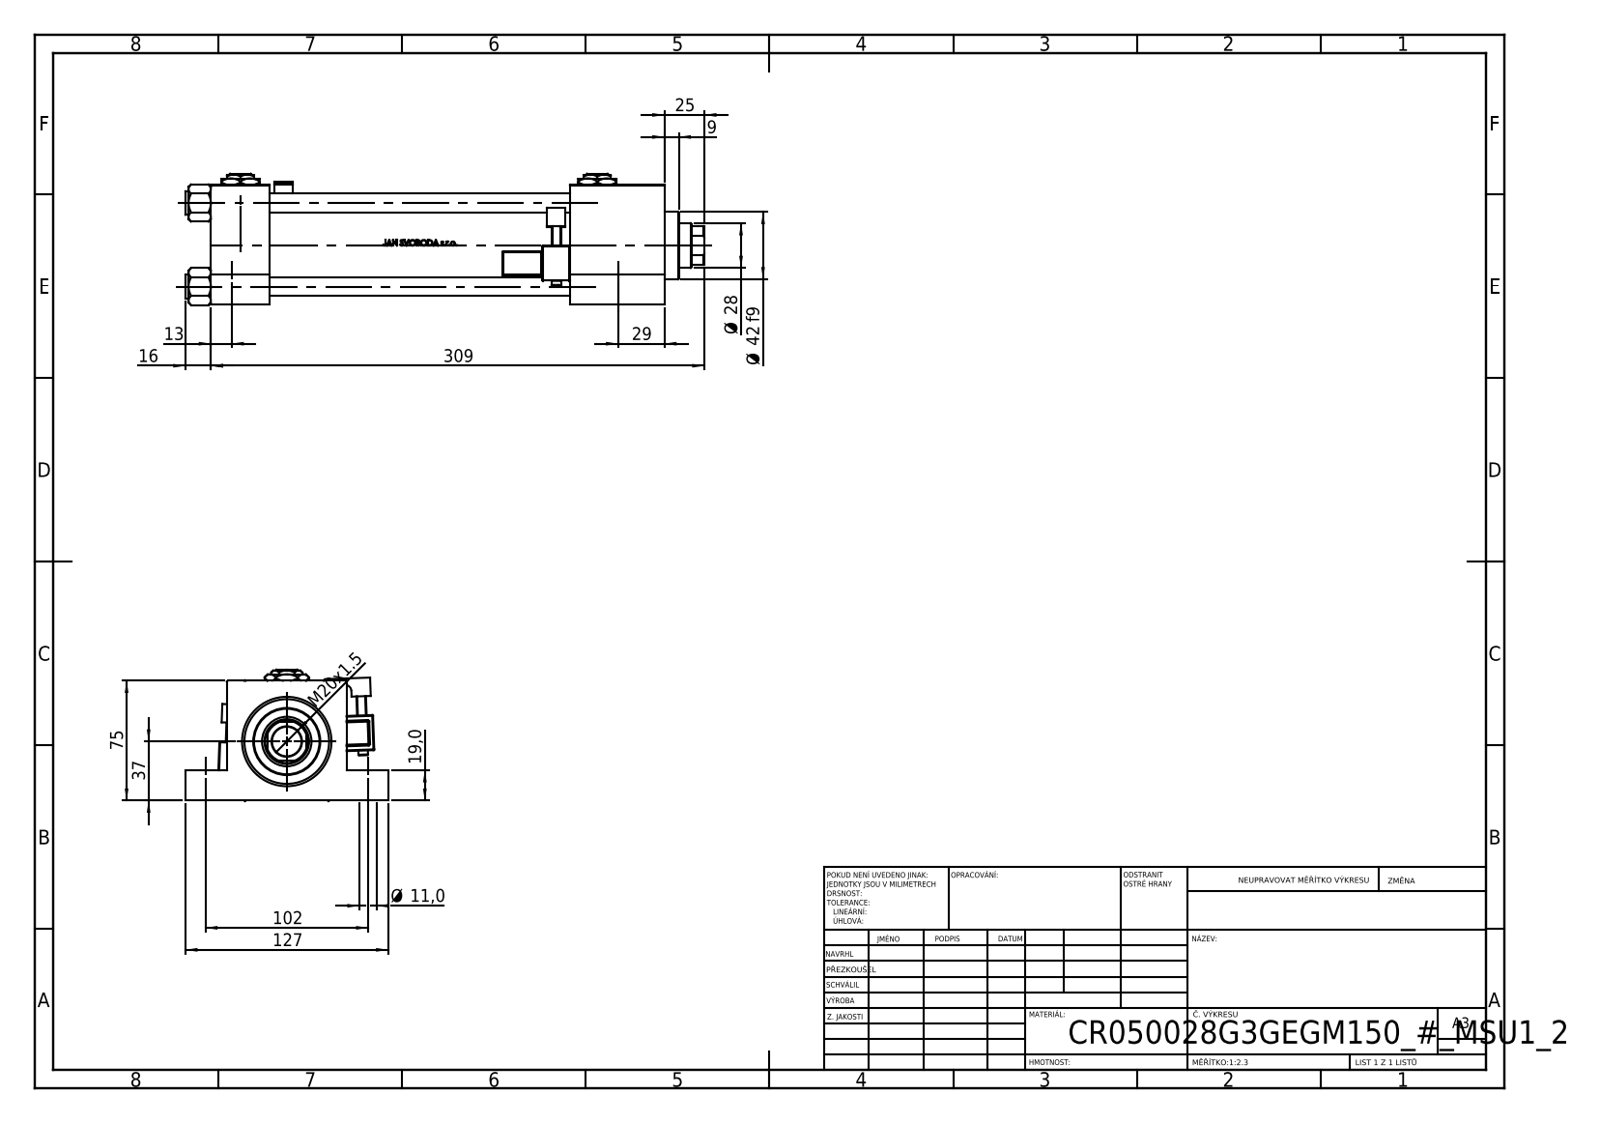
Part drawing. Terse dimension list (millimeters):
name: V215CR_MSU; V215CR_G_Body; V215CR_VCP_G; V215_VC_A (+3 more)
written by: SolidWorks 2019 (CONFIG_CONTROL_DESIGN)
unit: mm
bodies: 15 solids, 1326 faces (534 planar, 184 cylindrical, 608 other)
size: 325 × 127 × 82.27
volume: 1 018 000 mm³; area: 252 538 mm²
holes: 4× ⌀11, 4× ⌀12, 2× ⌀7, 2× ⌀20.96, 2× ⌀30, 1× ⌀18.5, 1× ⌀28, 1× ⌀31, 1× ⌀41, 1× ⌀50, 1× ⌀53
bosses: 4× ⌀15, 2× ⌀6, 1× ⌀56, 1× ⌀42
rounds: 48× R0.5, 2× R1, 2× R2.5, 2× R4, 1× R6, 1× R13.5
face distances: 75, 37, 284, 247, 225, 188, 59, 56, 19, 26
hole spacings: 52.3, 36.63, 37.34, 51.3, 52.63, 73.96, 102, 234.61
